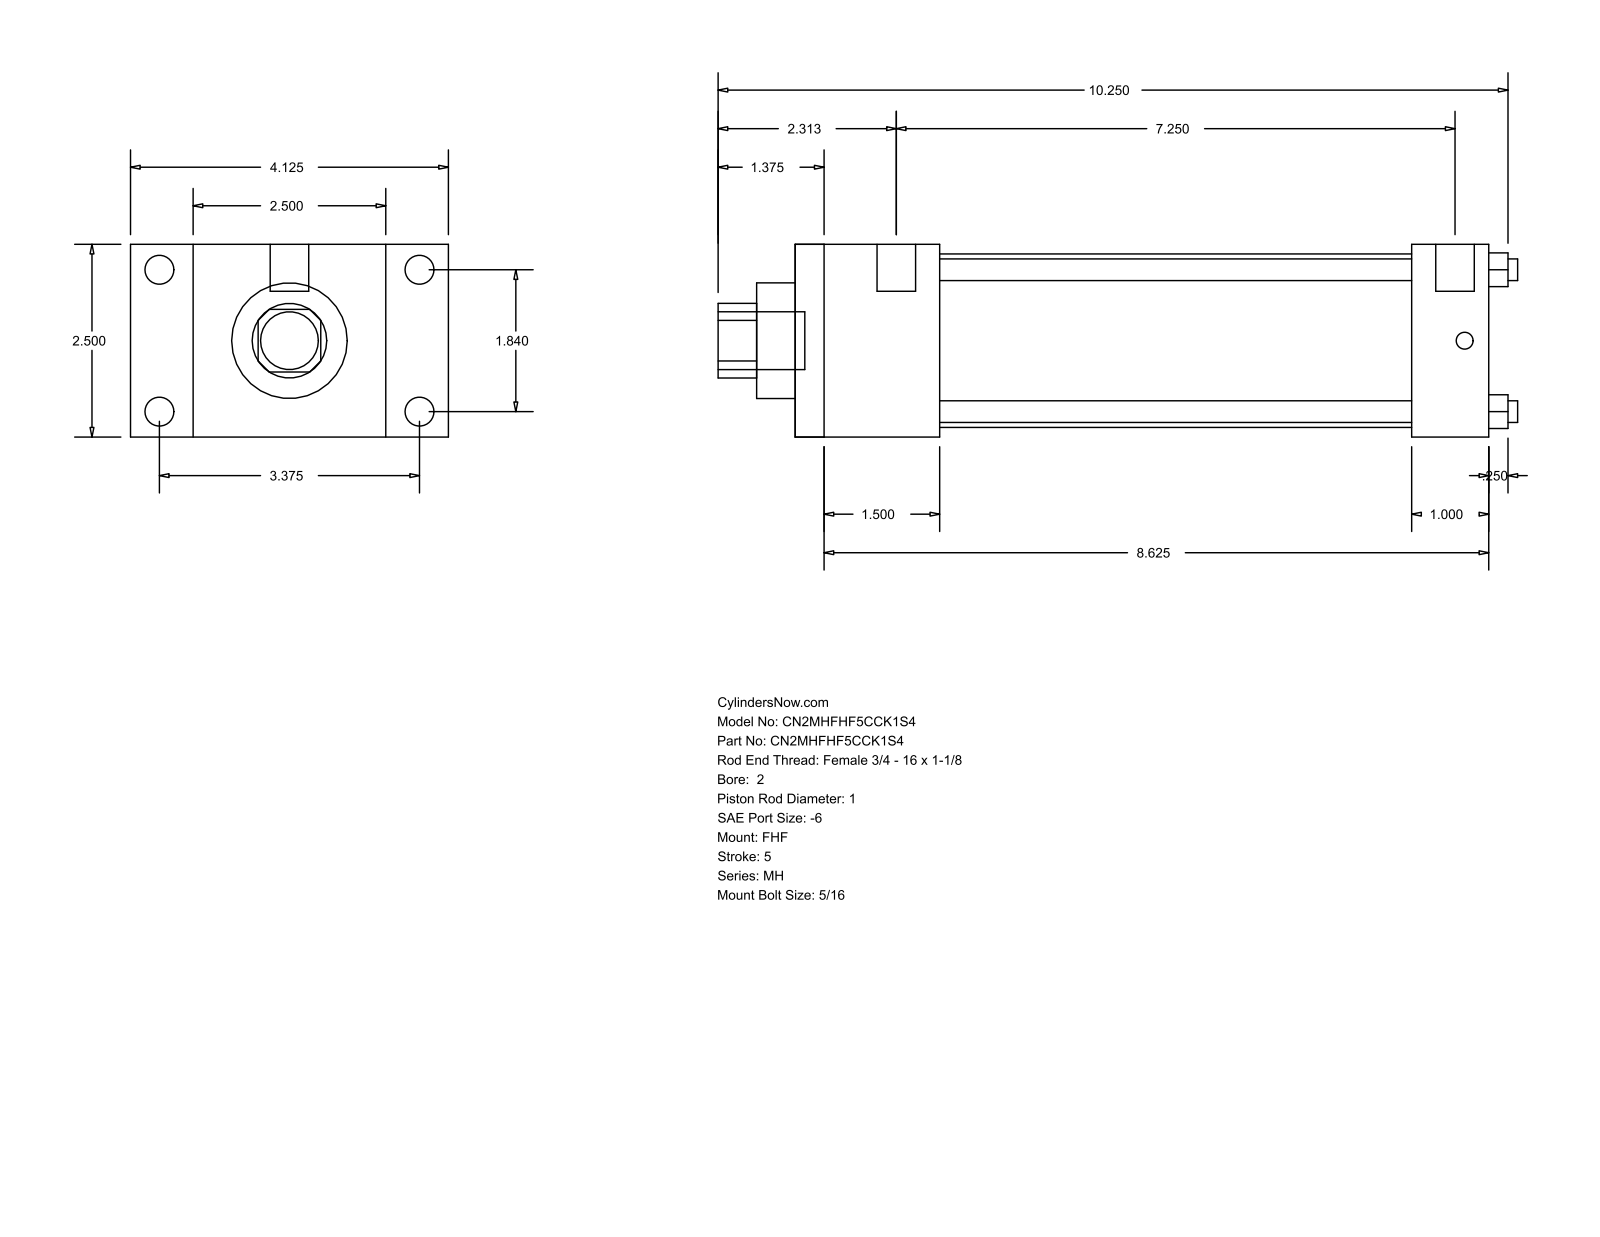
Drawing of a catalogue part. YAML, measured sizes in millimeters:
part_name: "MH_FHF__0200_1"
step_written_by: "GSSL Pune (CONFIG_CONTROL_DESIGN)"
units: millimeters
bodies: {solids: 0, faces: 88, planar: 60, cylindrical: 28, other: 0}
overall_size: [263.52, 104.78, 63.5]
round_holes:
  - {diameter: 7.14, count: 4}
  - {diameter: 25.4, count: 1}
  - {diameter: 38.1, count: 1}
  - {diameter: 57.15, count: 1}
round_bosses_or_shafts:
  - {diameter: 9.53, count: 4}
  - {diameter: 5.56, count: 4}
  - {diameter: 12.7, count: 2}
  - {diameter: 19.05, count: 1}
partial_cylinders:
  - {radius: 12.29, count: 1}
face_to_face_distances: [63.5, 228.6, 47.63, 180.97, 20.64, 84.14, 104.78, 25.4, 203.2, 155.57]
hole_center_spacings: [33.05, 46.74, 66.1]
